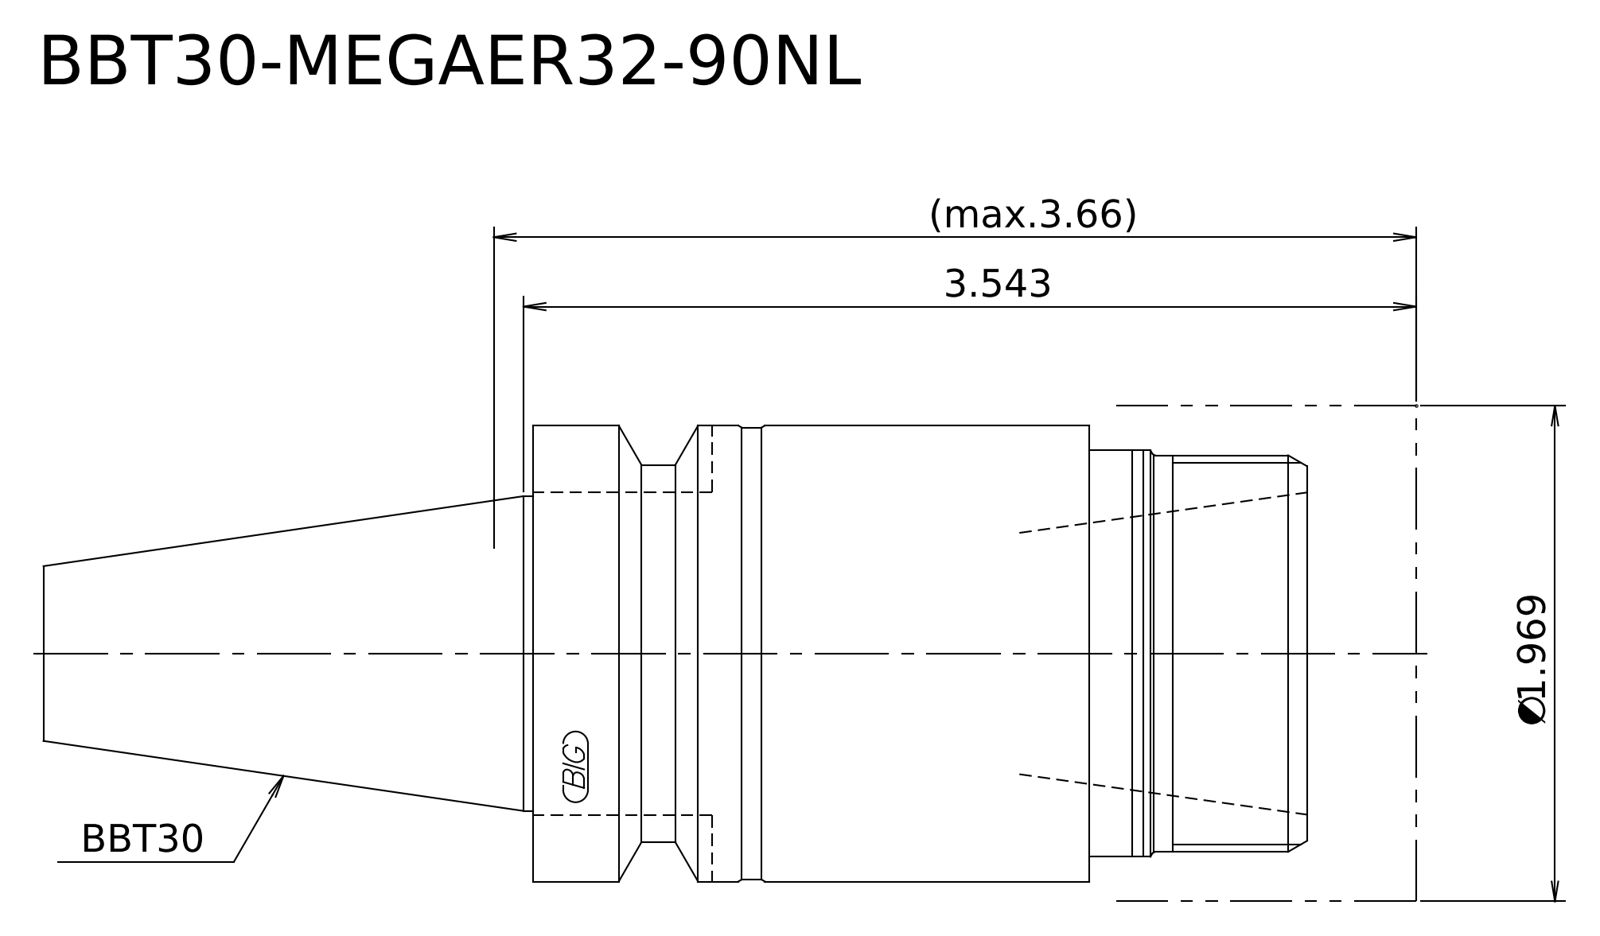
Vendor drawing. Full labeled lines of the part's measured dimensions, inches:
STEP written by: Kubotek KeyCreator 2011 V10.0.2 (22737) (automotive_design)
Units: inches
Bodies: 2 solids, 18 faces (6 planar, 7 cylindrical, 5 other)
Overall size (bounding box): 5.449 × 1.969 × 1.969
Volume: 12.32 in³ · Surface area: 41.16 in²
Round bosses / shafts (diameter × count): ⌀1.969 ×1, ⌀1.811 ×1, ⌀1.614 ×1, ⌀1.575 ×1, ⌀1.496 ×1, ⌀1.25 ×1
Main face-to-face distances: 1.189, 0.433, 0.756, 3.504, 3.071, 2.315, 1.299, 0.866, 0.11, 2.205
